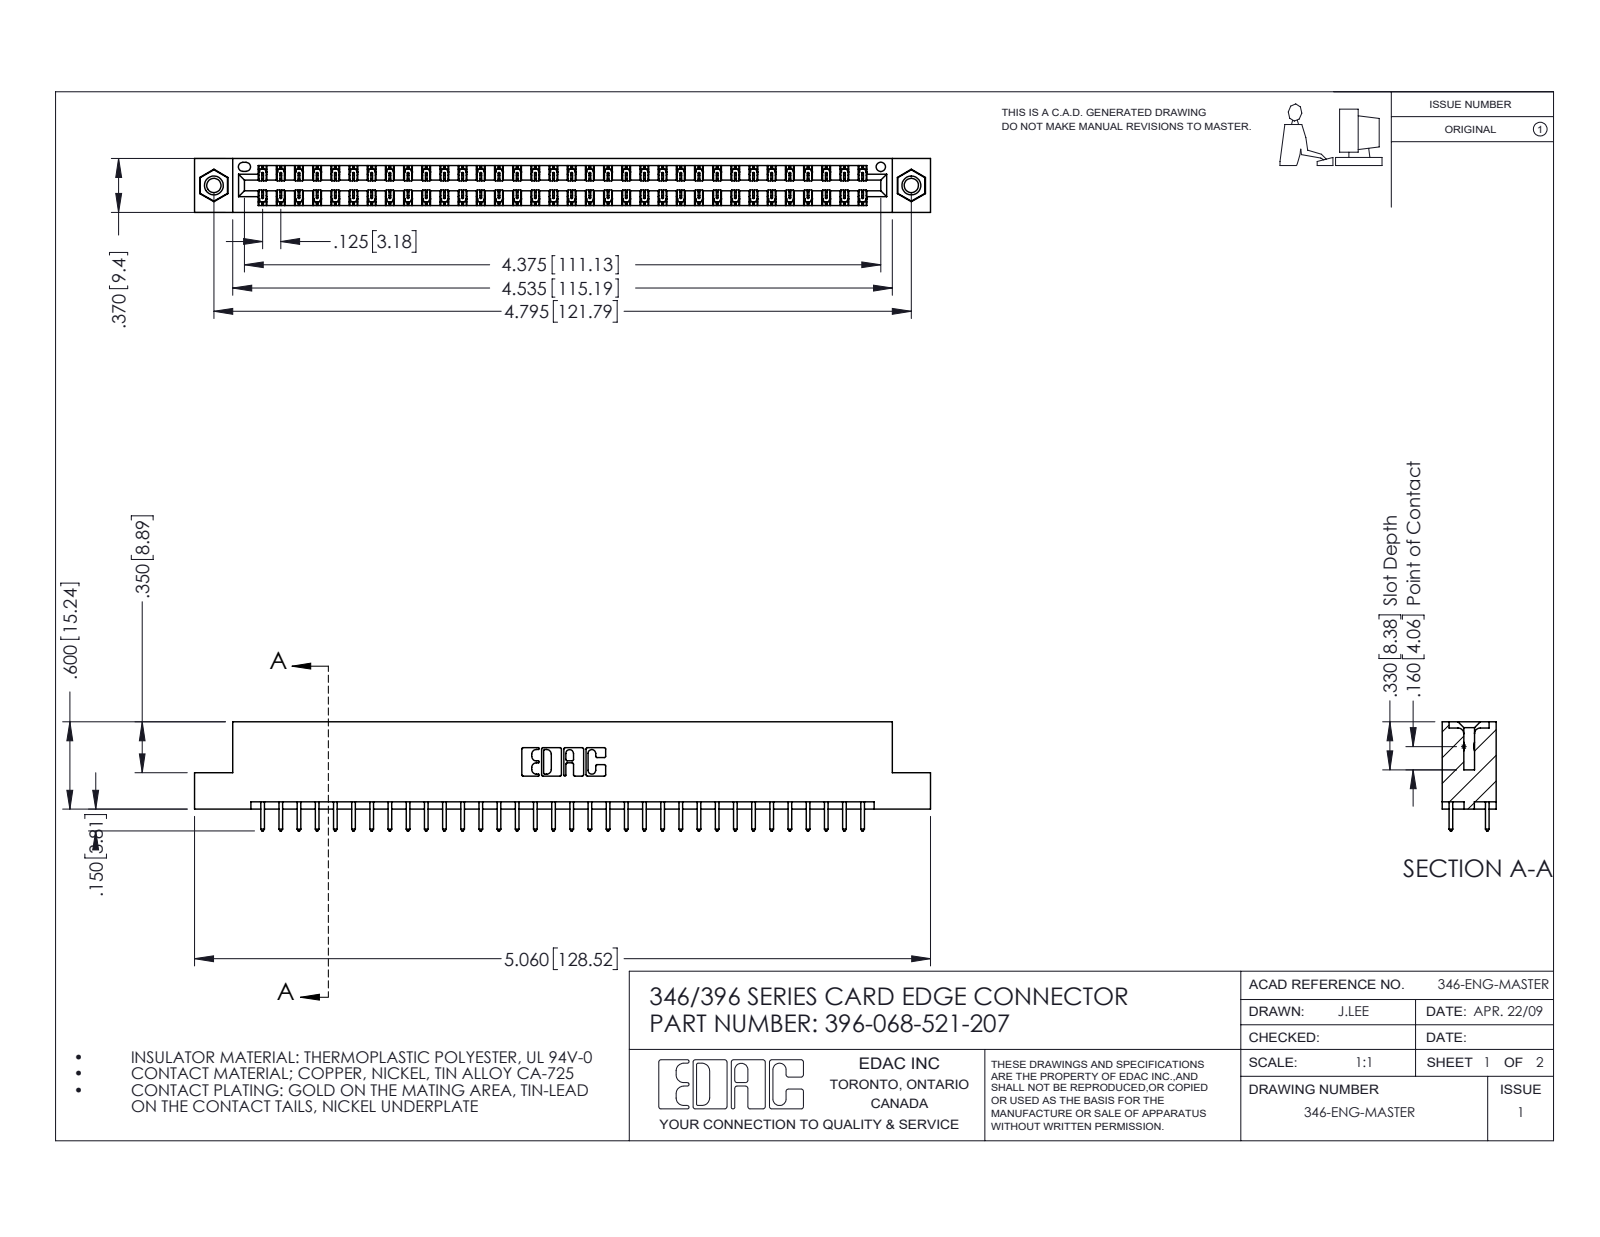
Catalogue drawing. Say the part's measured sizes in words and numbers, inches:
The part is named "345-292-001_345-293-121; 396-068-521-207; 346 Part_Flush Mounting Lugs - 0.156 Dia-TI; 345-250-001_345-250-005-103". Its 3-D file was written by "SolidWorks 2016 (CONFIG_CONTROL_DESIGN)". It is 71 solids with 3718 faces: 2488 planar, 1214 cylindrical and 16 other. Overall it measures 5.06 by 0.75 by 0.37 inches. Its volume is 0.758 cubic inches and its surface area 26.05 square inches. Round holes: 2 of diameter 0.098, 2 of diameter 0.125, 2 of diameter 0.156, 1 of diameter 0.064. Round bosses or shafts: 2 of diameter 0.155. Partial cylindrical surfaces (rounded edges, fillets, slot ends): 102 of radius 0.006, 68 of radius 0.01, 22 of radius 0.01, 6 of radius 0.007, 6 of radius 0.031, 3 of radius 0.026, 2 of radius 0.014, 2 of radius 0.022. The main face-to-face distances are 0.048, 0.322, 0.25, 0.37, 0.072, 0.298, 0.025, 0.275, 0.148, 0.222. The hole center spacings are 0.246, 4.587, 4.795.
